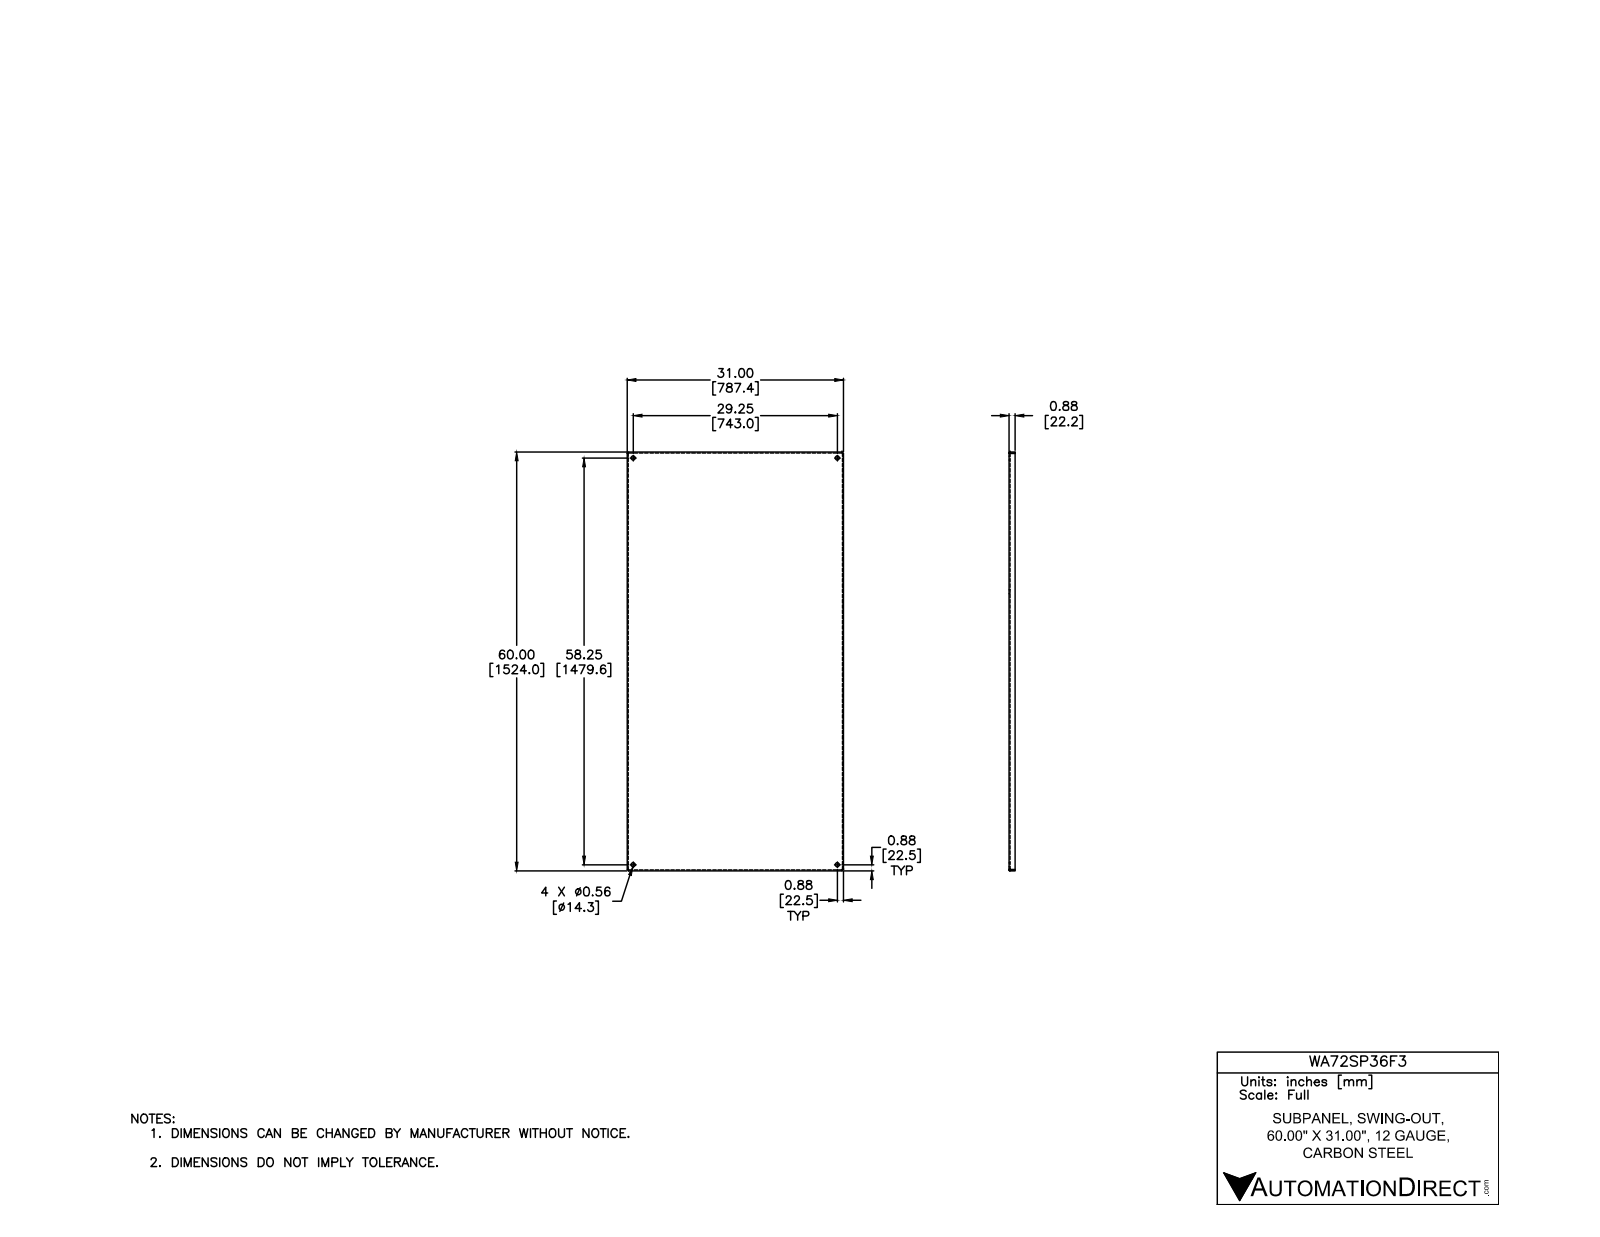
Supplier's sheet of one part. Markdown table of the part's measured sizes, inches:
| quantity | value |
| --- | --- |
| part name | WA60SP24F3-WA90SP36F4 |
| STEP written by | Autodesk Inventor 2012 (AUTOMOTIVE_DESIGN) |
| units | inches |
| bodies | 1 solid, 42 faces (22 planar, 12 cylindrical, 8 other) |
| overall size | 60 × 31 × 0.875 |
| volume | 186.9 in³ |
| surface area | 4 006 in² |
| round holes (diameter × count) | 0.563 × 4 |
| partial cylindrical surfaces (radius × count) | 0.031 × 4, 0.125 × 4 |
| main face-to-face distances | 0.094, 30.906, 59.906, 31, 30.813, 59.813, 60, 0.781, 0.875, 0.16 |
| hole center spacings | 29.25, 58.25, 65.182 |
